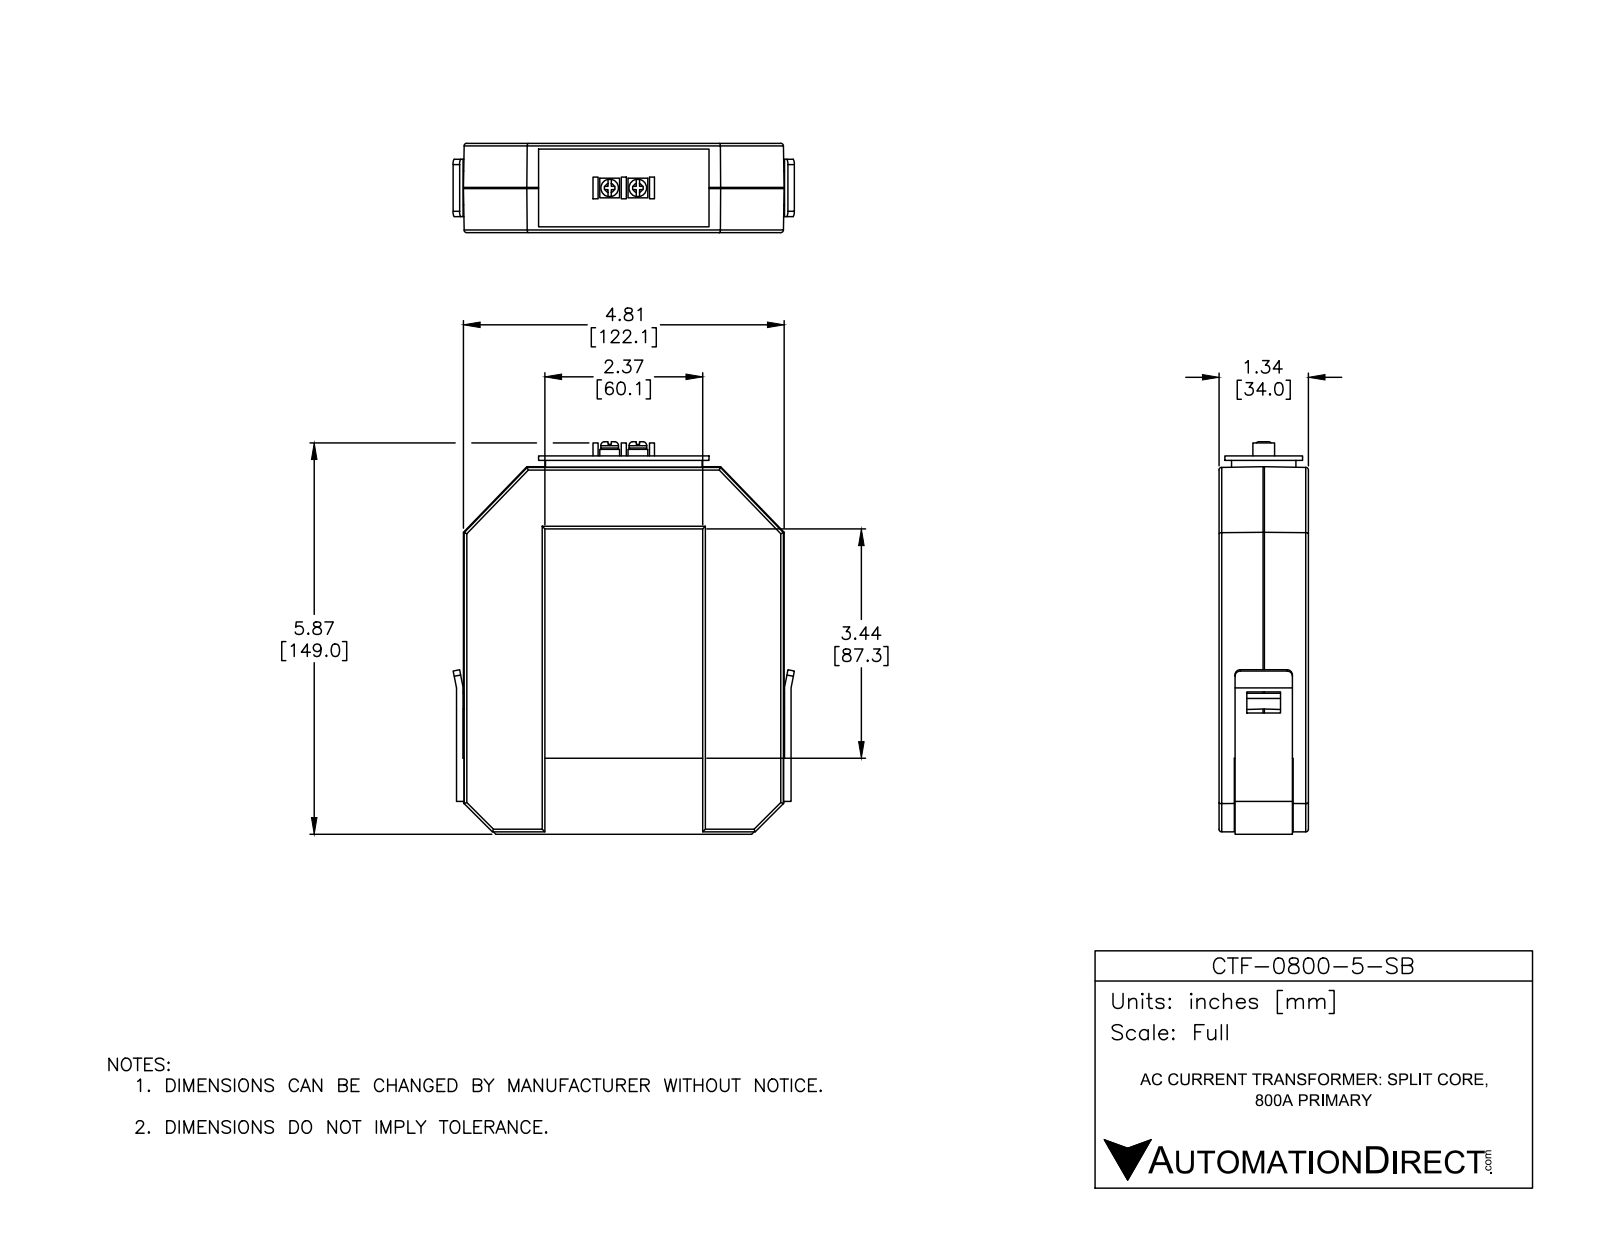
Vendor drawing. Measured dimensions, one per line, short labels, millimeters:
name: CTF-0800-5-SB
written by: SolidWorks 2016 (AUTOMOTIVE_DESIGN)
unit: mm
bodies: 8 solids, 194 faces (154 planar, 32 cylindrical, 8 other)
size: 149.4 × 129.9 × 34
volume: 368 200 mm³; area: 63 760 mm²
bosses: 2× ⌀6.7
rounds: 22× R1, 4× R2
face distances: 34, 6.1, 27.9, 21.9, 5.8, 28.2, 22.1, 60.1, 122.1, 28.9
